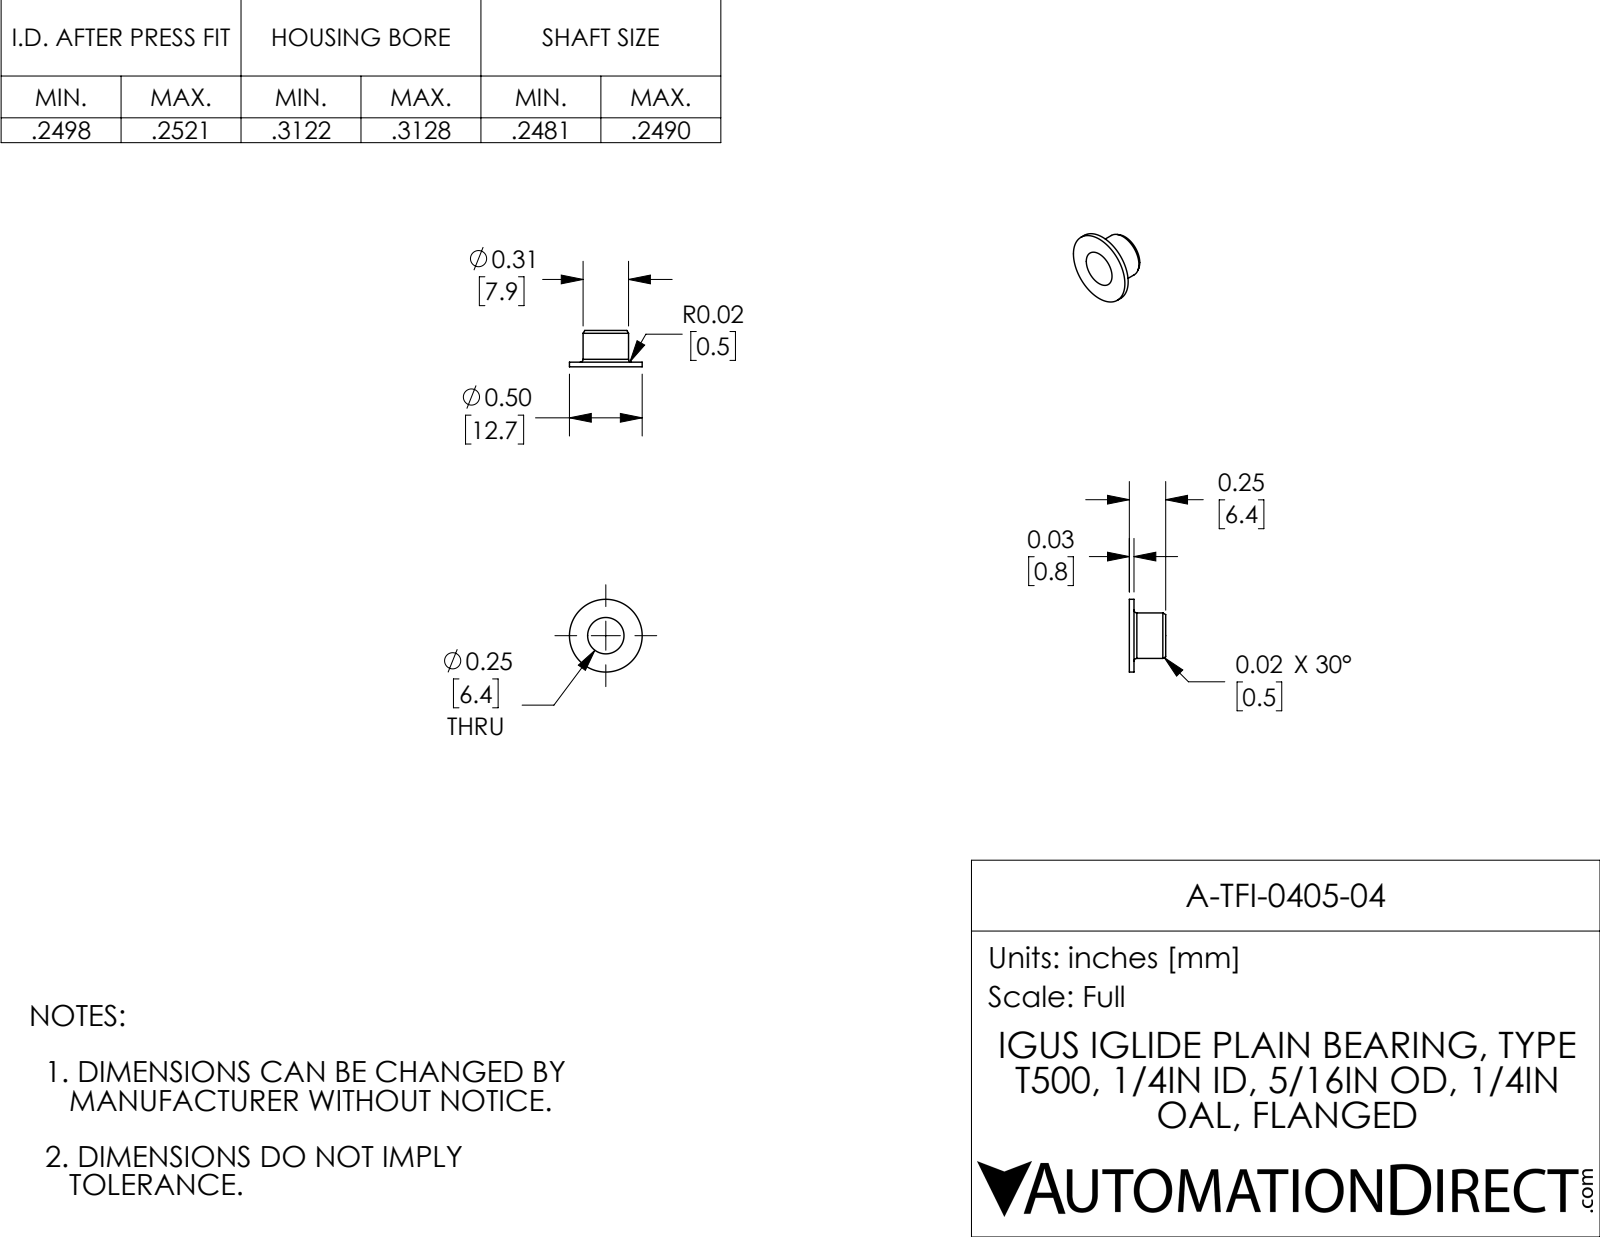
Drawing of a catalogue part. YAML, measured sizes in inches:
part_name: "A-TFI-0405-04"
step_written_by: "SolidWorks 2017 (AUTOMOTIVE_DESIGN)"
units: inches
bodies: {solids: 1, faces: 13, planar: 3, cylindrical: 6, other: 4}
overall_size: [0.5, 0.5, 0.25]
volume: 0.011
surface_area: 0.738
round_holes:
  - {diameter: 0.25, count: 1}
round_bosses_or_shafts:
  - {diameter: 0.5, count: 1}
  - {diameter: 0.313, count: 1}
face_to_face_distances: [0.032, 0.25, 0.218]
